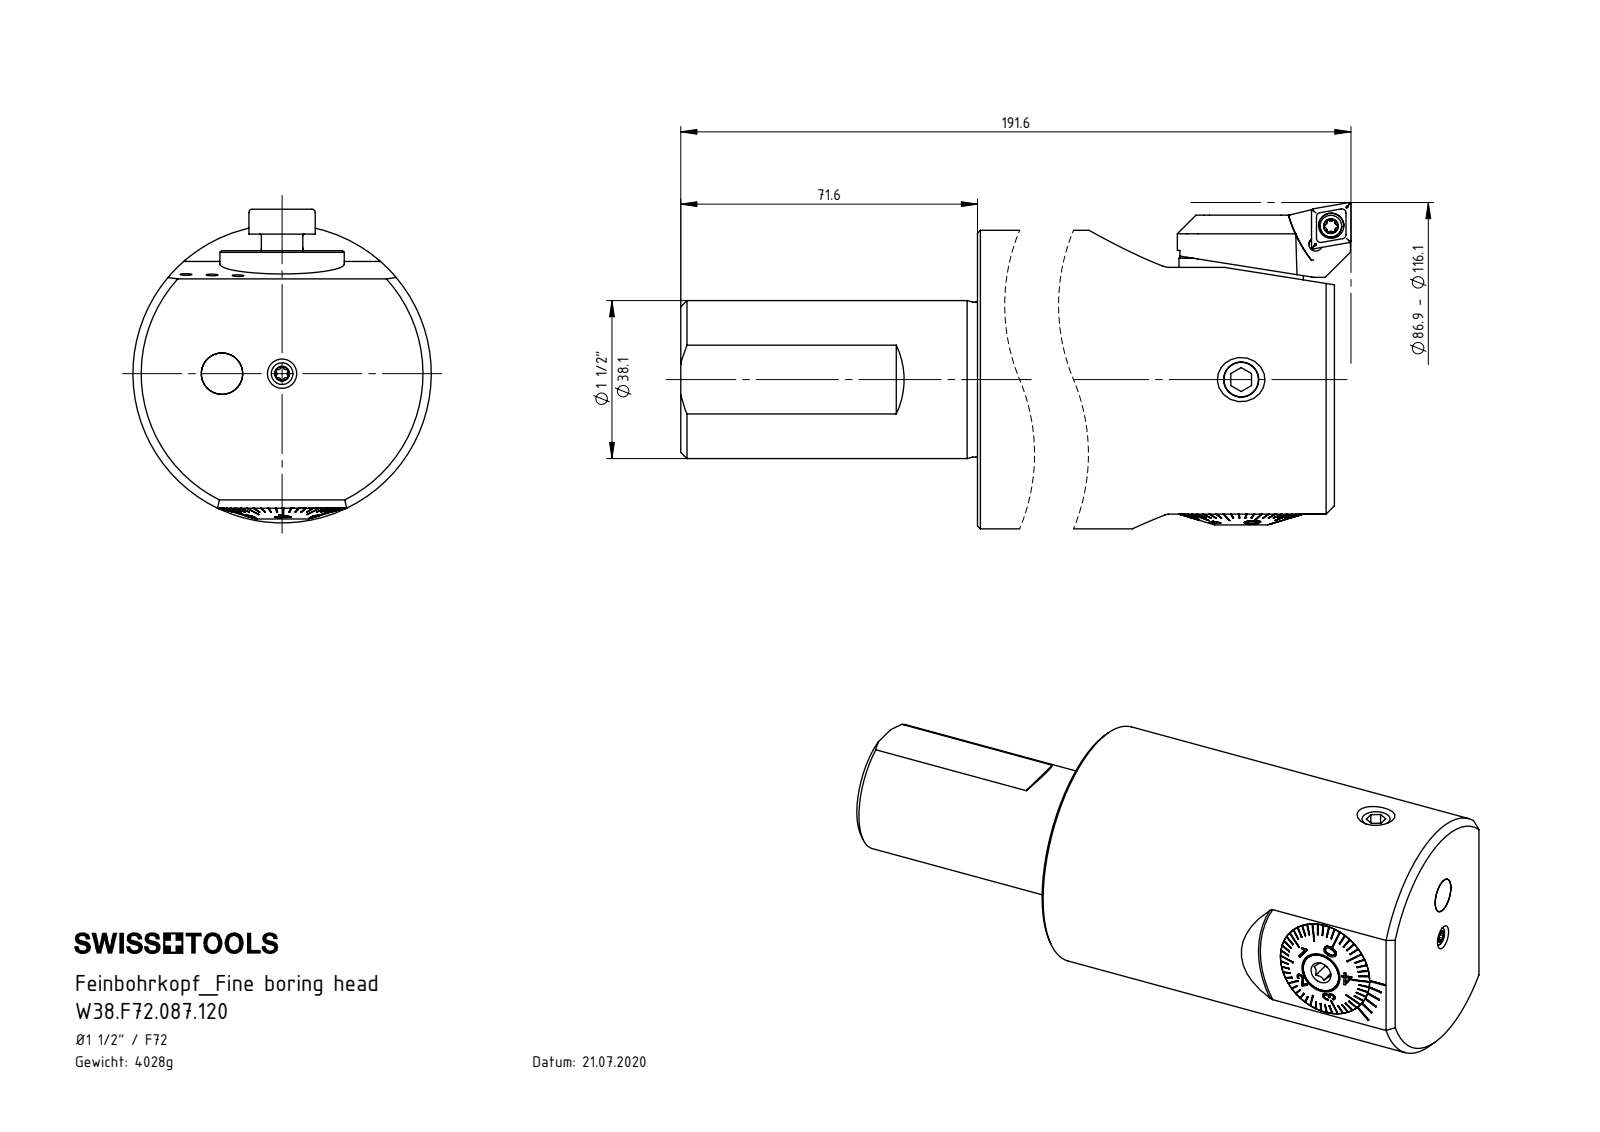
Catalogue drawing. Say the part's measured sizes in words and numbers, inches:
The part is named "W38.F72.087.120; Klebstoff D10; A55-BG2.013.005_C; DIN 3771 - 25x1.5 (+8 more)". Its 3-D file was written by "SolidWorks 2022 (CONFIG_CONTROL_DESIGN)". It is 13 solids with 703 faces: 300 planar, 136 cylindrical and 267 other. Overall it measures 7.386 by 2.979 by 2.835 inches. Its volume is 31.46 cubic inches and its surface area 113 square inches. Round holes: 3 of diameter 0.098, 3 of diameter 0.165, 2 of diameter 0.13, 2 of diameter 0.335, 1 of diameter 0.197, 1 of diameter 0.315, 1 of diameter 0.394, 1 of diameter 0.421, 1 of diameter 0.449, 1 of diameter 0.472, 1 of diameter 0.488, 1 of diameter 0.512. Round bosses or shafts: 2 of diameter 0.394, 1 of diameter 2.835, 1 of diameter 1.5, 1 of diameter 1.472, 1 of diameter 1.181, 1 of diameter 1.18, 1 of diameter 1.177, 1 of diameter 0.984. Partial cylindrical surfaces (rounded edges, fillets, slot ends): 6 of radius 0.013, 6 of radius 0.023, 6 of radius 0.098, 4 of radius 0.079, 3 of radius 0.126, 2 of radius 0.02, 1 of radius 0.039, 1 of radius 0.138. The main face-to-face distances are 4.567, 2.819, 7.386, 2.087, 0.256, 2.343, 0.098, 2.296, 0.209, 0.047. The hole center spacings are 0.571, 0.707, 0.78, 1.142.
